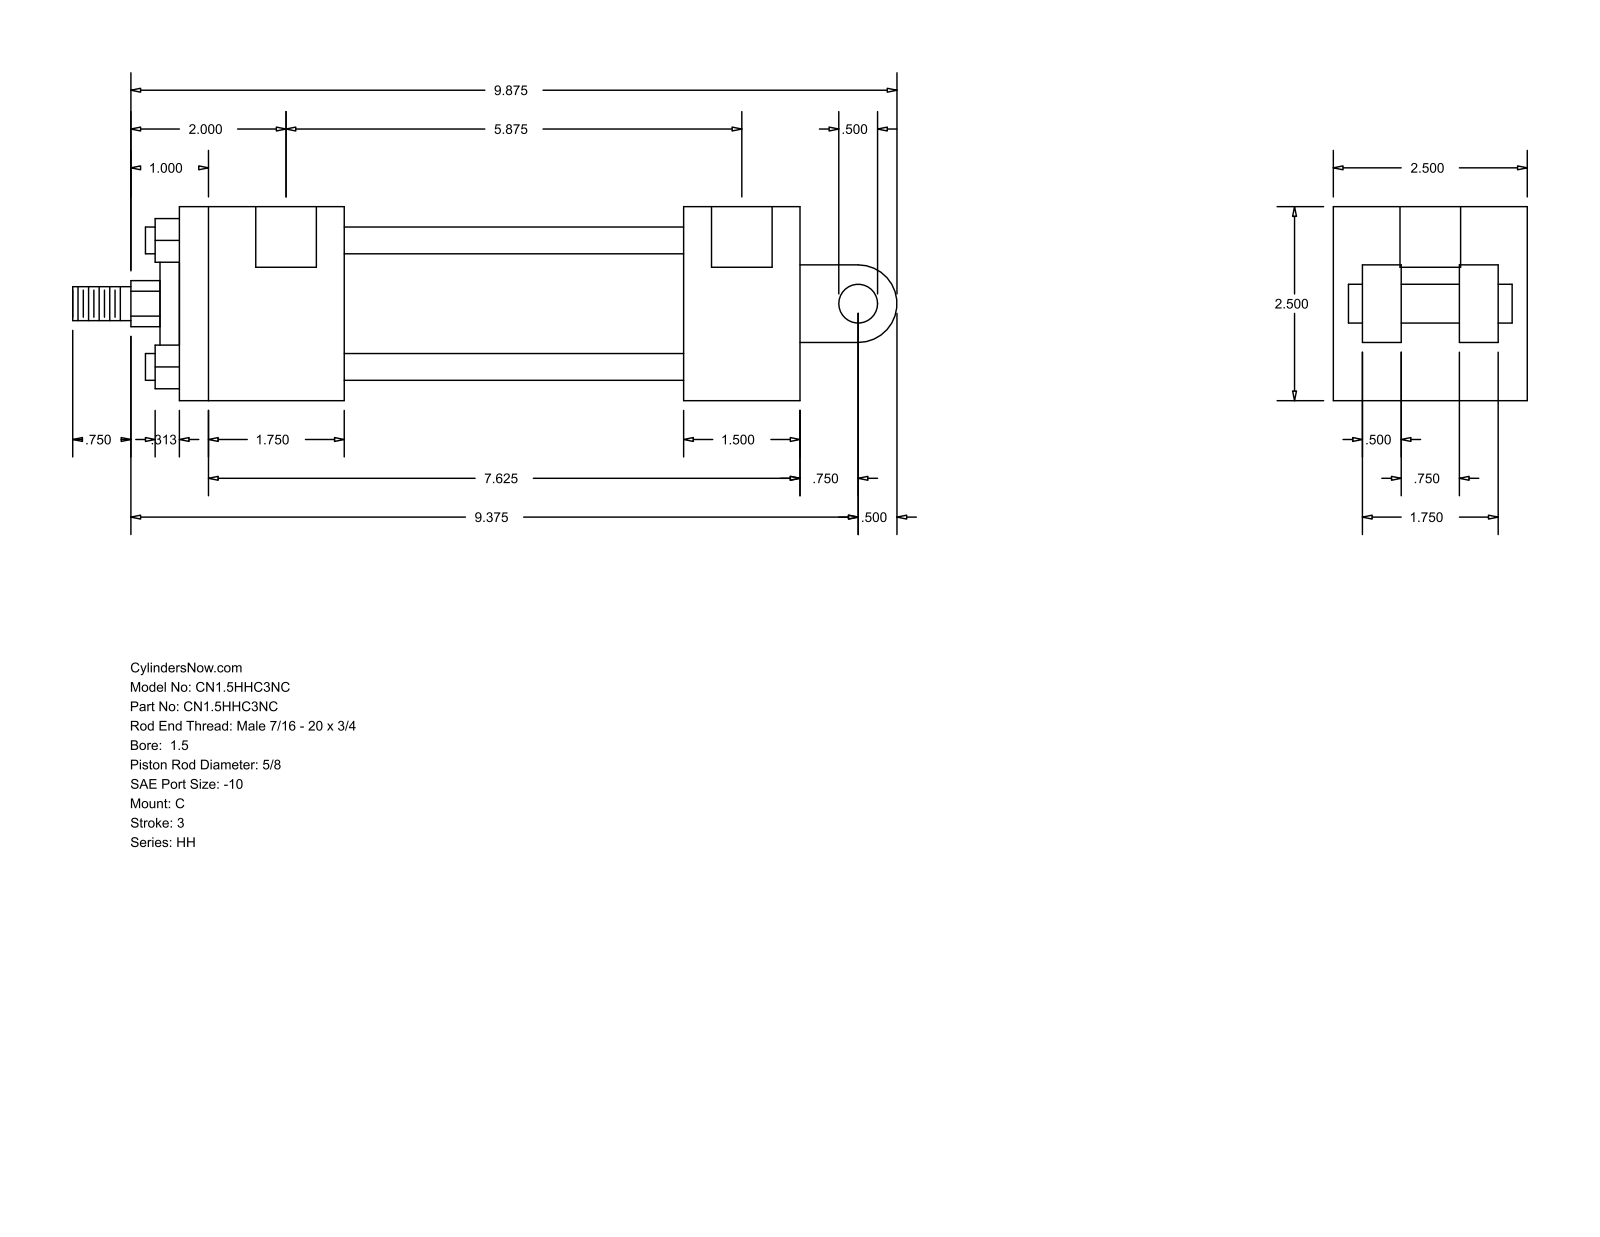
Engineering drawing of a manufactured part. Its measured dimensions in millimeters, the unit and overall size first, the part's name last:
Units: millimetres
Overall size (bounding box): 269.88 × 63.5 × 63.5
Round holes (diameter × count): ⌀5.56 ×4, ⌀19.84 ×2
Round bosses / shafts (diameter × count): ⌀8.76 ×4, ⌀44.45 ×1, ⌀28.57 ×1, ⌀15.88 ×1, ⌀12.7 ×1, ⌀11.11 ×1
Partial cylindrical surfaces — rounded edges, fillets, slot ends (radius × count): R7.54 ×1, R12.7 ×1
Main face-to-face distances: 63.5, 203.19, 38.1, 53.97, 165.09, 111.12, 149.22, 12.7, 19.05, 22.22
Hole centre spacings: 152.4, 1.58, 1.59, 149.23, 150.81, 150.82
Bodies: 0 solids, 99 faces (70 planar, 29 cylindrical, 0 other)
Part name (STEP PRODUCT): HH_C__0150_0.625
STEP written by: GSSL Pune (CONFIG_CONTROL_DESIGN)
